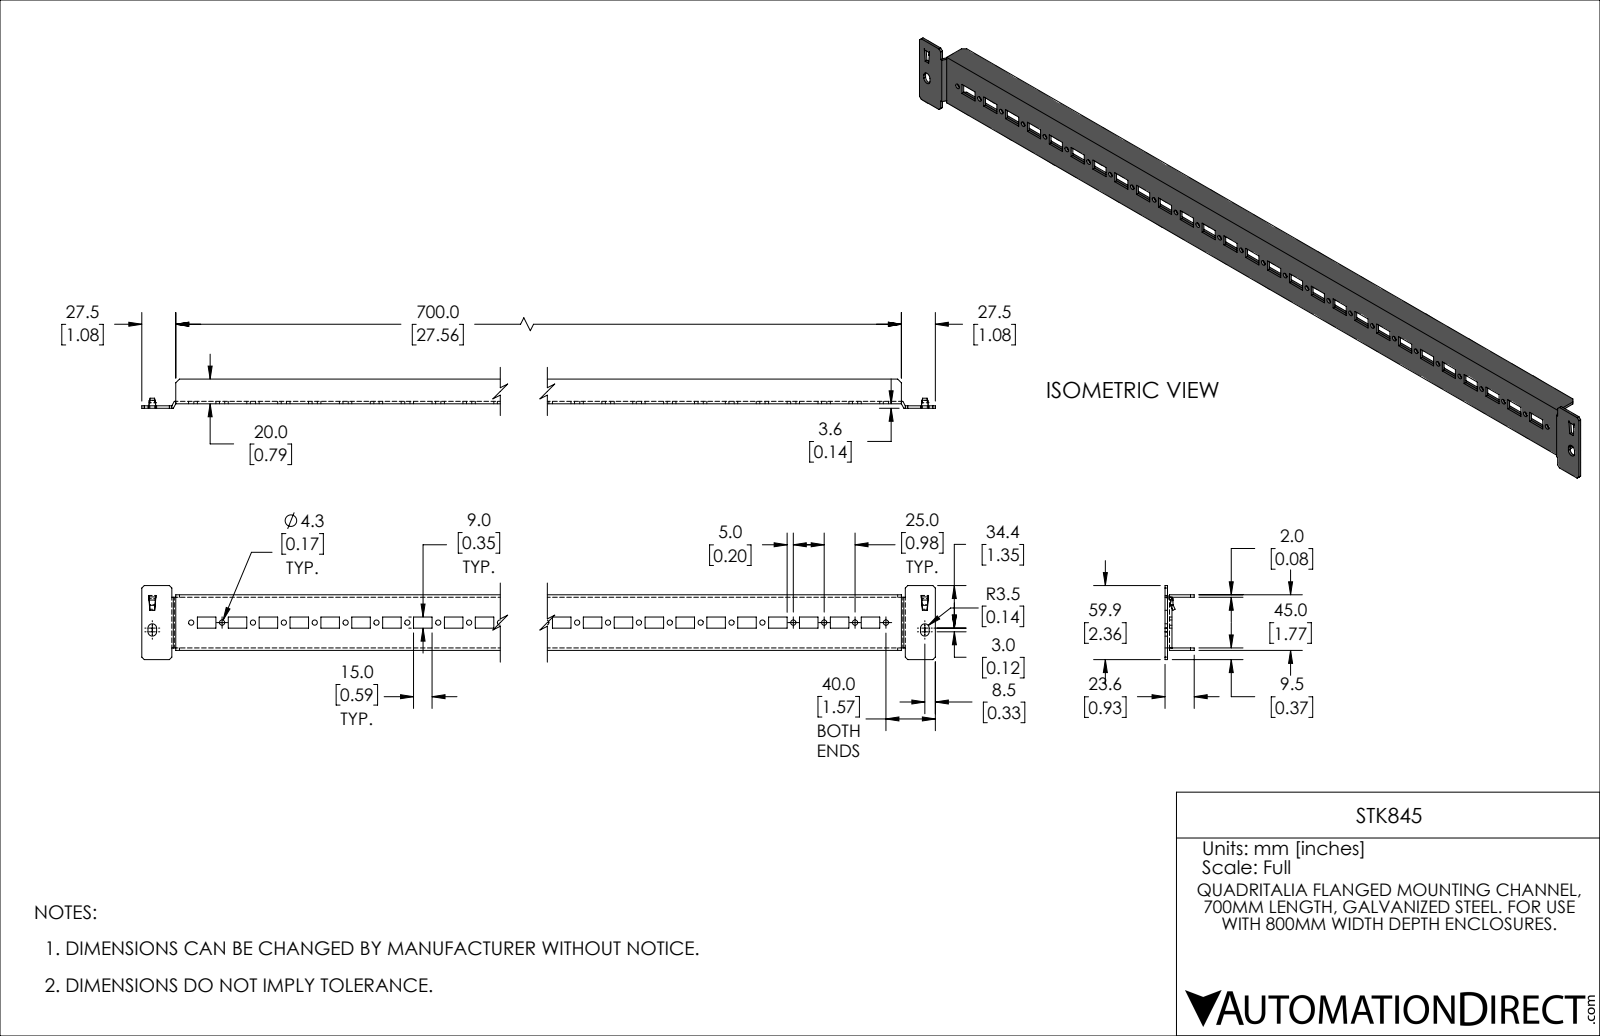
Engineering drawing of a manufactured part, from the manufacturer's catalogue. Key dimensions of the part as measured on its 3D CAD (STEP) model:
Part name (STEP PRODUCT): STK845
STEP written by: SolidWorks 2021 (CONFIG_CONTROL_DESIGN)
Units: inches
Bodies: 1 solid, 246 faces (202 planar, 32 cylindrical, 12 other)
Overall size (bounding box): 29.724 × 2.359 × 0.93
Volume: 6.819 in³ · Surface area: 184.3 in²
Round holes (diameter × count): ⌀0.167 ×28
Partial cylindrical surfaces — rounded edges, fillets, slot ends (radius × count): R0.138 ×4
Main face-to-face distances: 0.079, 1.693, 1.772, 1.614, 0.143, 0.709, 0.787, 0.221, 0.93, 0.064
Hole centre spacings: 0.984, 1.969, 2.953, 3.937, 4.921, 5.906, 6.89, 7.874
